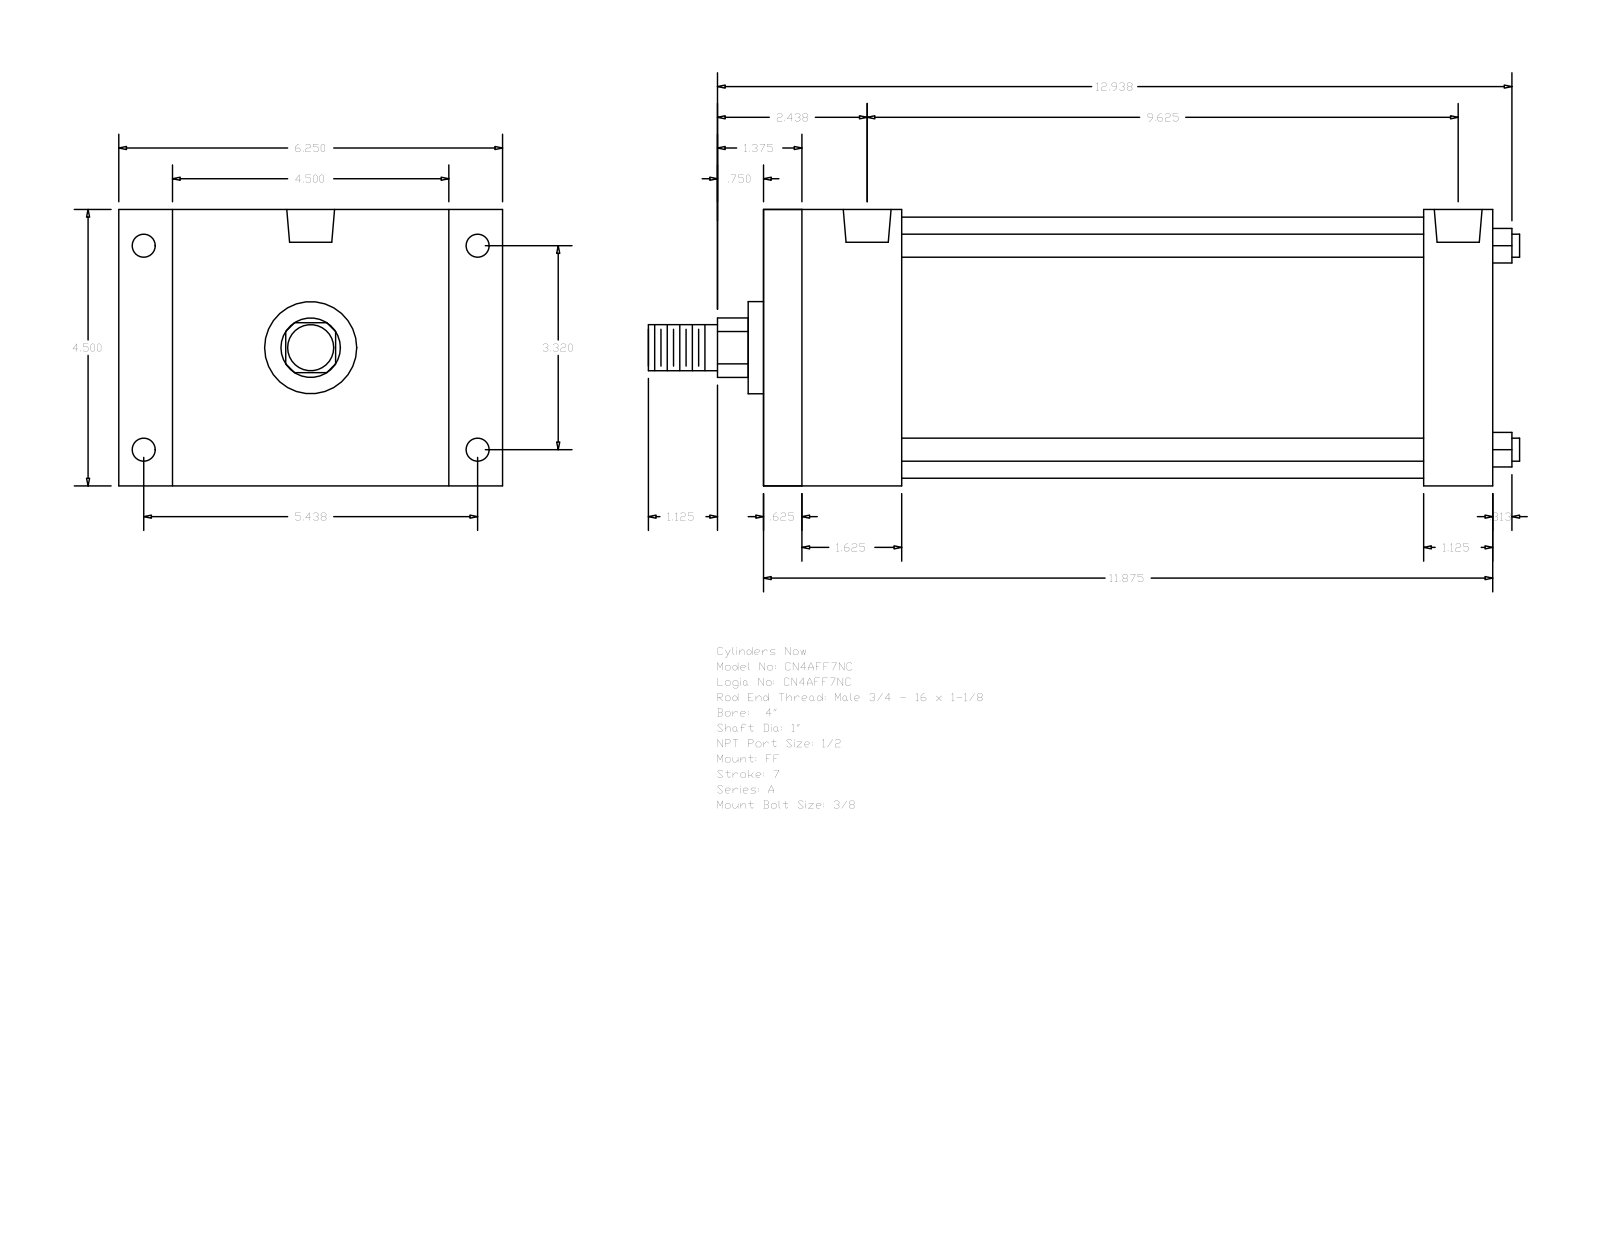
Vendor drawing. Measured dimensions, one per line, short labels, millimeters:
name: A_FF__0400_1
written by: GSSL Pune (CONFIG_CONTROL_DESIGN)
unit: mm
bodies: 0 solids, 92 faces (64 planar, 28 cylindrical, 0 other)
size: 360.36 × 158.75 × 114.3
holes: 4× ⌀8.73, 4× ⌀9.53, 2× ⌀19.77
bosses: 4× ⌀9.53, 1× ⌀107.95, 1× ⌀38.1, 1× ⌀25.4, 1× ⌀19.05
rounds: 1× R12.29
face distances: 114.3, 301.63, 15.87, 285.76, 22.23, 136.53, 273.05, 257.18, 28.58, 57.15
hole spacings: 3.18, 84.32, 138.12, 161.82, 238.12, 241.3, 244.48
